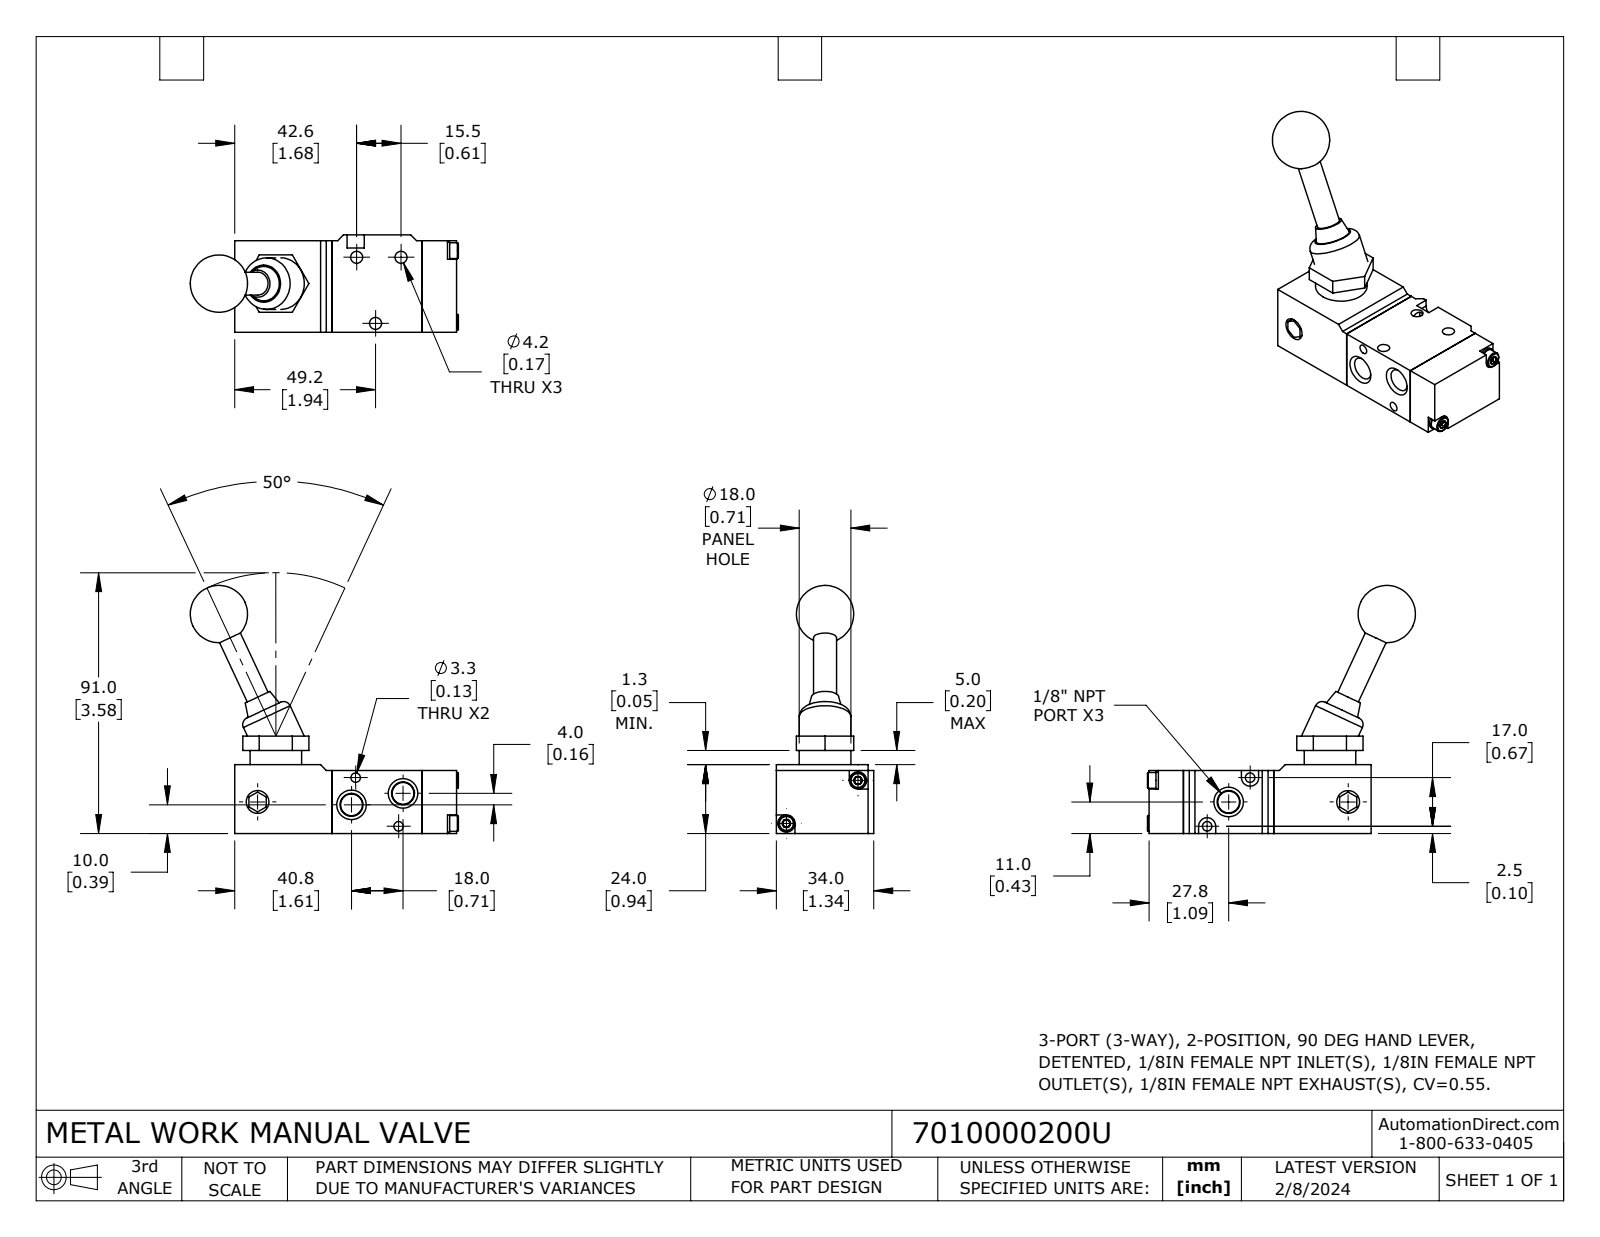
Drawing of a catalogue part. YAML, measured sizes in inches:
part_name: "7010000200U"
step_written_by: "SolidWorks 2023 (CONFIG_CONTROL_DESIGN)"
units: inches
bodies: {solids: 8, faces: 190, planar: 100, cylindrical: 44, other: 46}
overall_size: [3.685, 3.409, 1.339]
volume: 4.096
surface_area: 30.32
round_holes:
  - {diameter: 0.165, count: 3}
  - {diameter: 0.118, count: 2}
  - {diameter: 0.13, count: 2}
  - {diameter: 0.313, count: 1}
round_bosses_or_shafts:
  - {diameter: 0.709, count: 2}
  - {diameter: 0.236, count: 2}
  - {diameter: 0.217, count: 2}
  - {diameter: 0.315, count: 1}
partial_cylinders:
  - {radius: 0.118, count: 2}
face_to_face_distances: [1.339, 0.866, 1.24, 1.26, 0.079, 0.472, 2.579, 0.945, 1.713, 3.051]
hole_center_spacings: [0.61, 0.893, 0.946, 0.975, 1.148, 1.389, 1.968]
